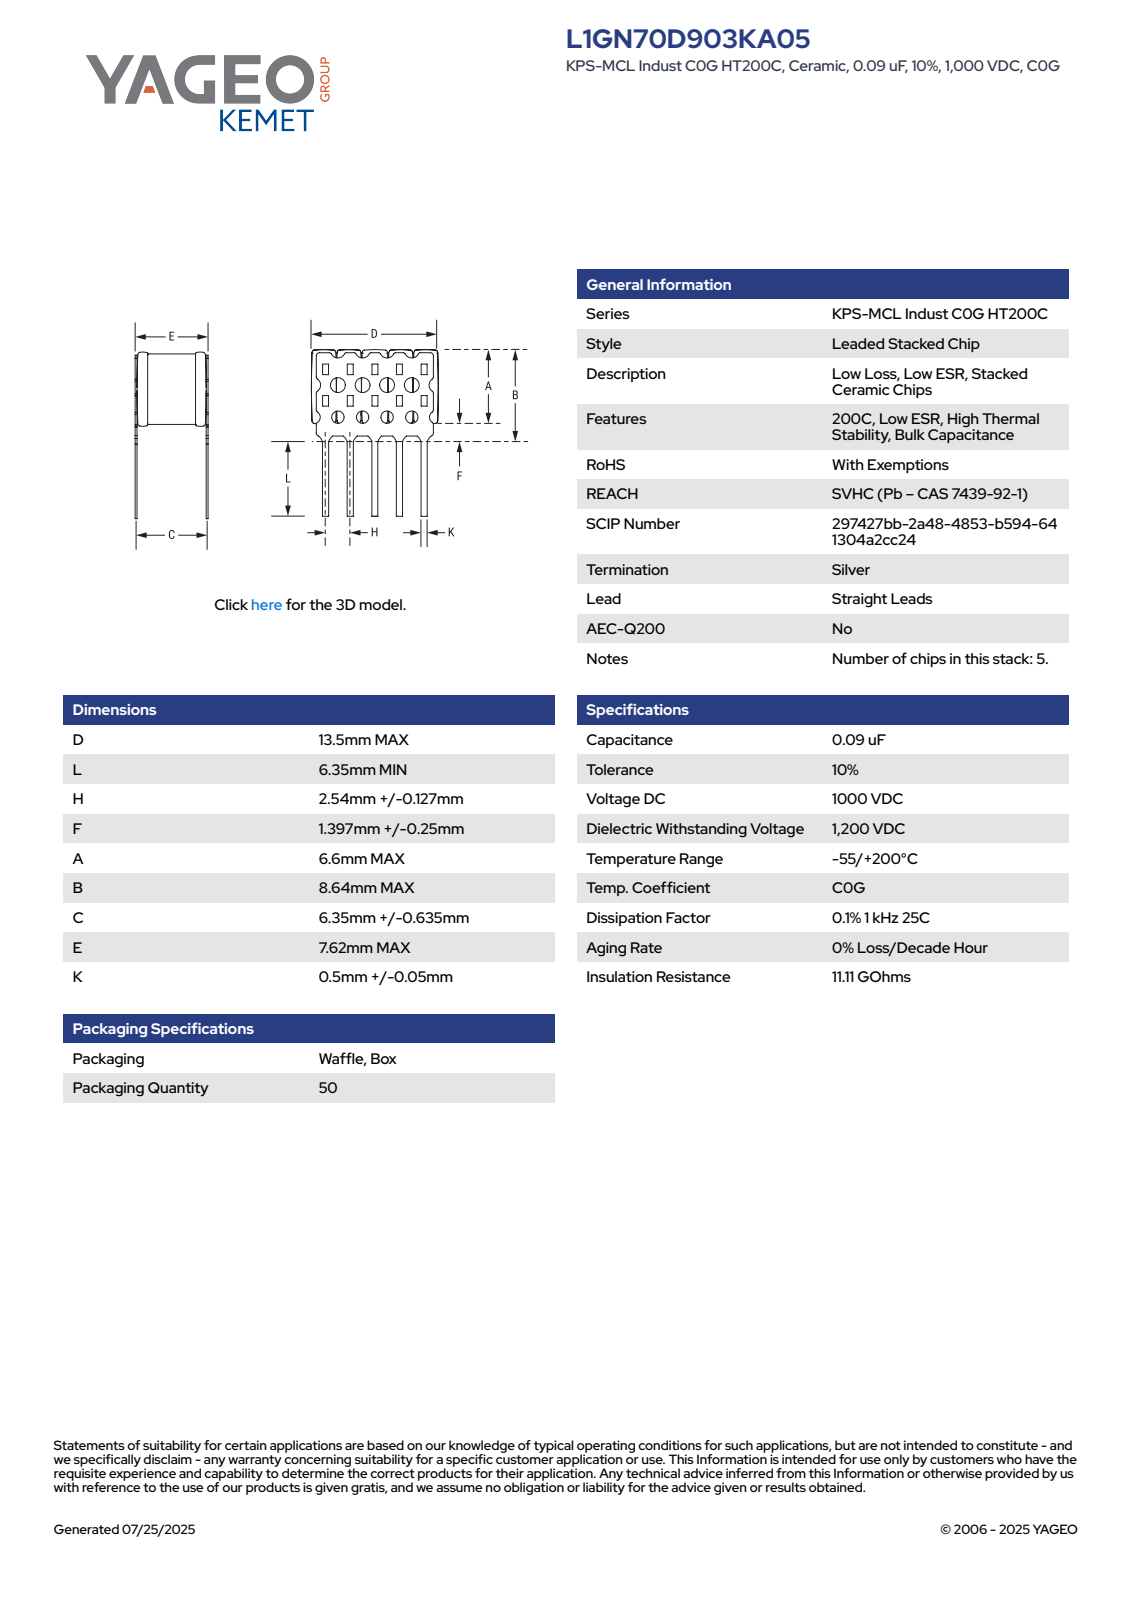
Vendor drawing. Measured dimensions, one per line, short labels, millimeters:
name: CCSS_KLSS5_D13.5L6.35H2.667F1.647A6.6B8.64C6.985E7.62K0.55
written by: SolidWorks 2014 (AUTOMOTIVE_DESIGN)
unit: mm
bodies: 7 solids, 238 faces (238 planar, 0 cylindrical, 0 other)
size: 14.22 × 9.74 × 8.64
volume: 652 mm³; area: 807 mm²
face distances: 5.69, 6.99, 2.84, 5.49, 2.85, 2.64, 8.54, 6.89, 5.89, 8.33
